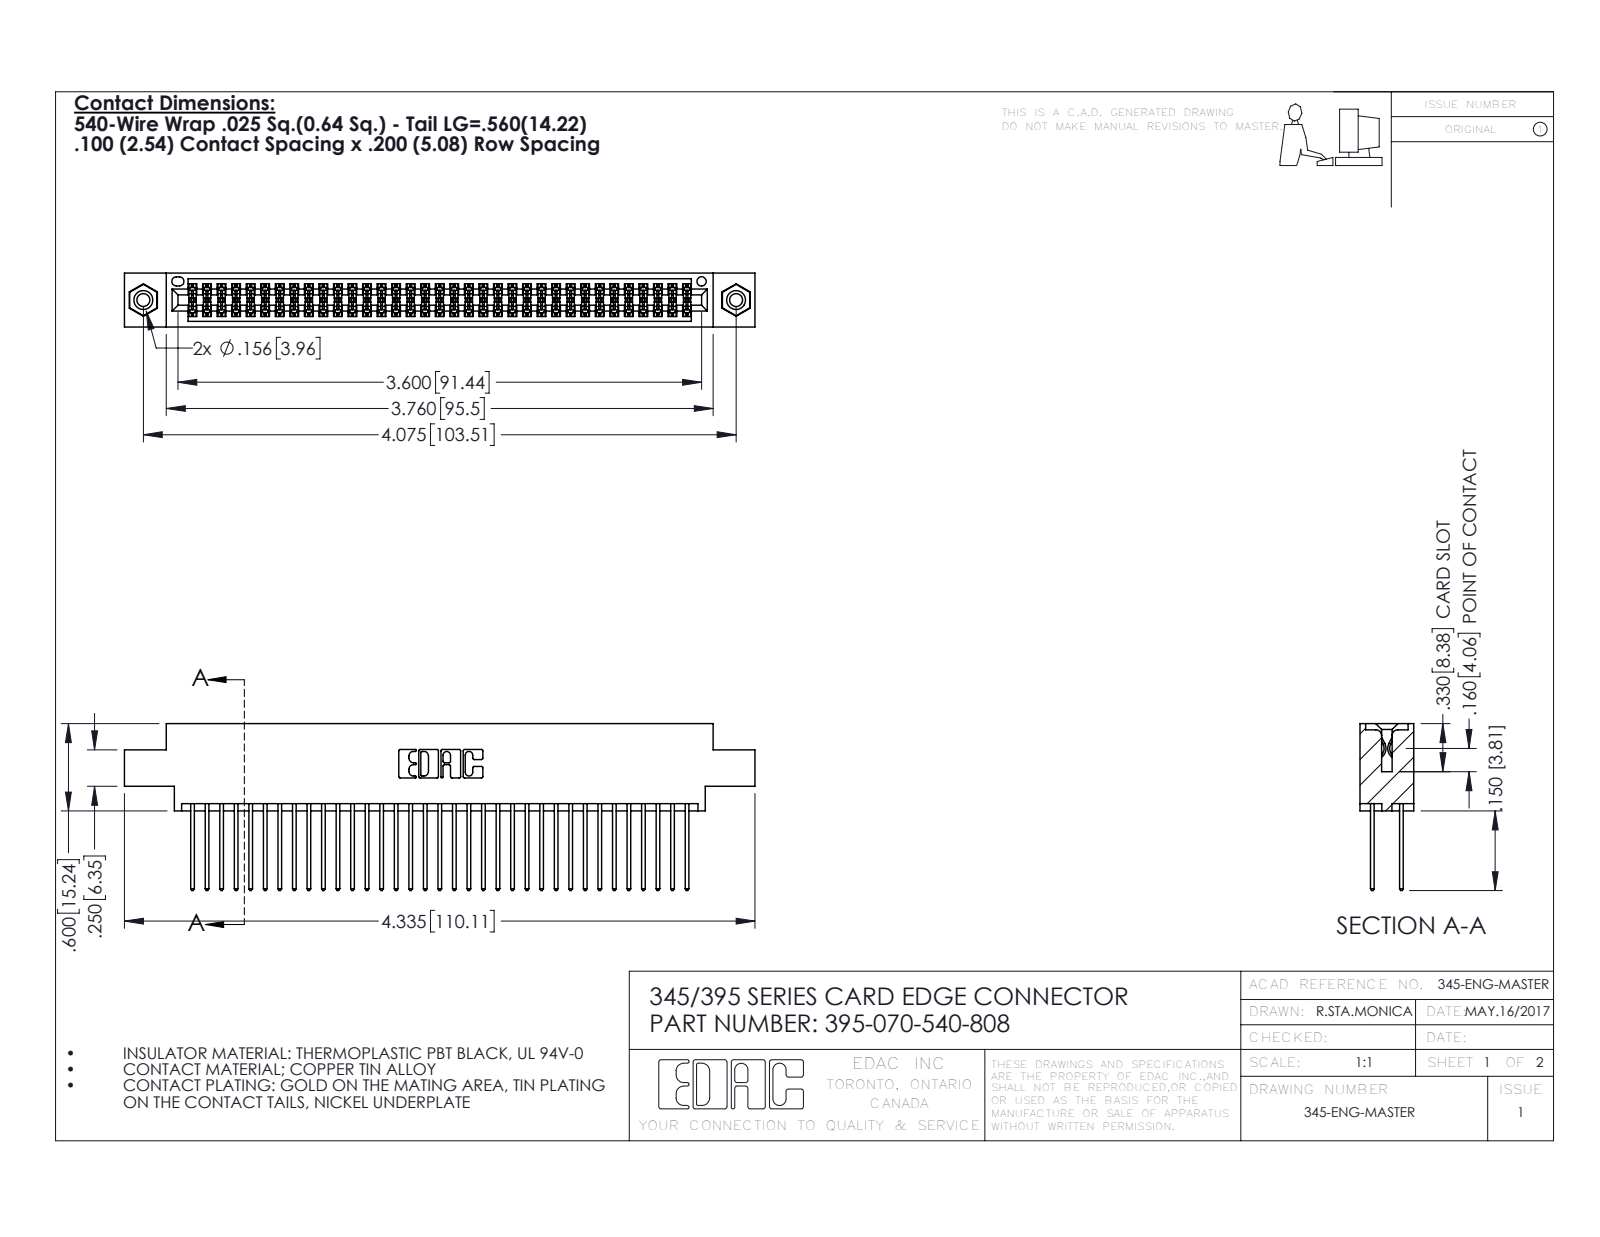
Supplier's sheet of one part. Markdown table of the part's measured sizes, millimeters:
| quantity | value |
| --- | --- |
| part name | 345-250-001_345-250-003-102; 395-070-540-808; 345-292-001_345-293-140; 345 Part_0.170 Offset - 0.156 Dia-TI |
| STEP written by | SolidWorks 2016 (CONFIG_CONTROL_DESIGN) |
| units | millimeters |
| bodies | 73 solids, 3690 faces (2426 planar, 1248 cylindrical, 16 other) |
| overall size | 110.1 × 29.1 × 9.4 |
| volume | 10 800 mm³ |
| surface area | 17 180 mm² |
| round holes (diameter × count) | 2.3 × 2, 3.2 × 2, 4 × 2, 1.6 × 1 |
| round bosses / shafts (diameter × count) | 3.9 × 2 |
| partial cylindrical surfaces (radius × count) | 0.2 × 105, 0.3 × 70, 0.3 × 22, 0.2 × 6, 0.8 × 6, 0.7 × 3, 0.4 × 2, 0.5 × 2 |
| main face-to-face distances | 1.8, 7.6, 5.1, 2.5, 6.9, 0.6, 9.4, 5.7, 4.4, 3.8 |
| hole center spacings | 6.9, 97.5, 103.5 |
